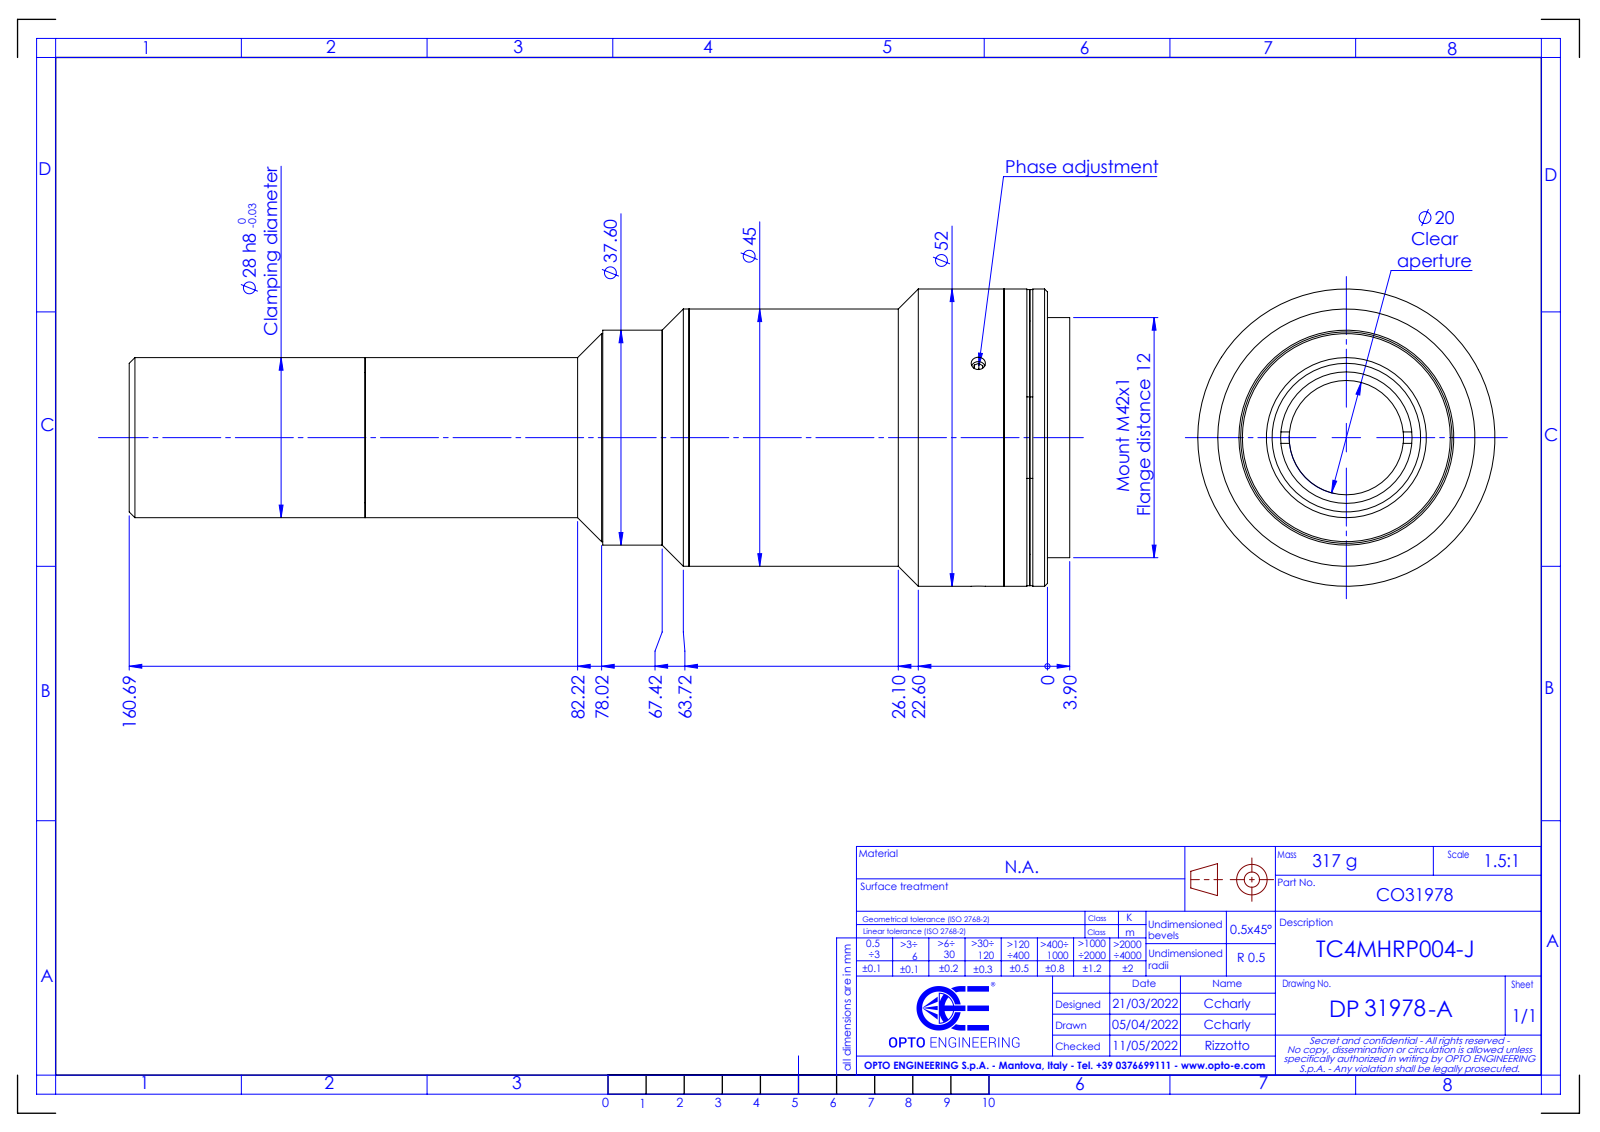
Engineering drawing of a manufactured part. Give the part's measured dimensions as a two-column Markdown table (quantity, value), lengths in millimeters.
| quantity | value |
| --- | --- |
| part name | DP31978-A_TC4MHRP004-J |
| STEP written by | SolidWorks 2021 (CONFIG_CONTROL_DESIGN) |
| units | millimeters |
| bodies | 0 solids, 92 faces (36 planar, 38 cylindrical, 18 other) |
| overall size | 164.59 × 52 × 52 |
| round holes (diameter × count) | 2.5 × 3, 20 × 1, 23 × 1, 38 × 1, 41 × 1 |
| round bosses / shafts (diameter × count) | 52 × 1, 51.8 × 1, 45 × 1, 42 × 1, 37.6 × 1, 36.4 × 1, 28 × 1 |
| main face-to-face distances | 0.5, 0.54, 5.04, 4, 1.04, 7.6, 3.6, 2.56, 4.5, 3.1 |
